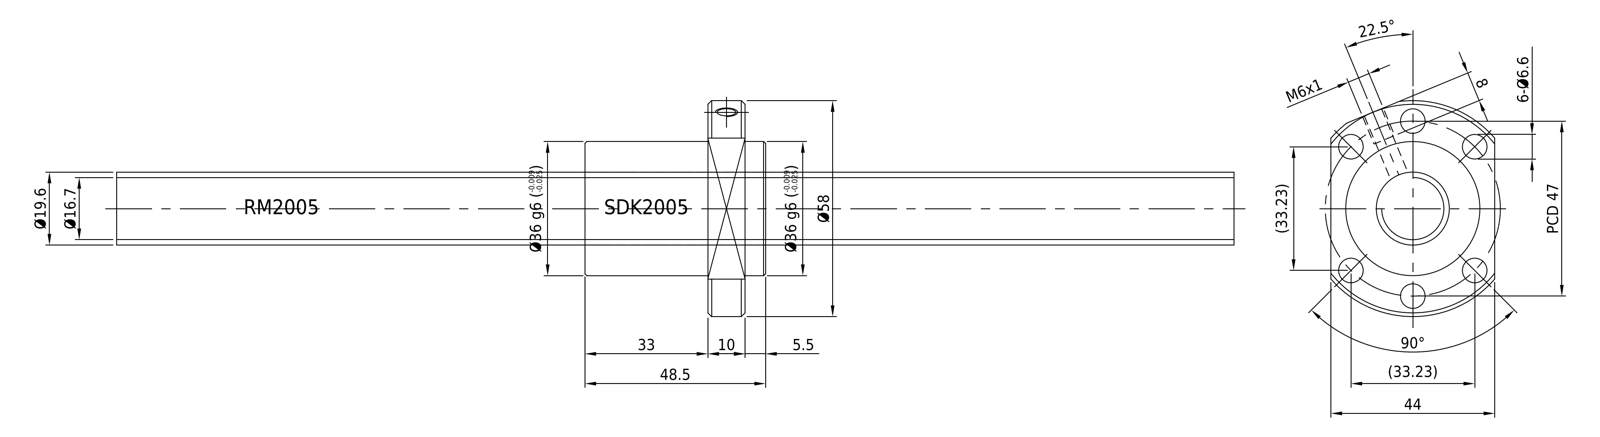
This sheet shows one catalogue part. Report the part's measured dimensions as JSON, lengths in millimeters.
{"part_name": "SDK2005; RM2005", "step_written_by": "SolidWorks 2013 (CONFIG_CONTROL_DESIGN)", "units": "millimeters", "bodies": {"solids": 2, "faces": 46, "planar": 9, "cylindrical": 27, "other": 10}, "overall_size": [300, 58, 44], "volume_mm3": 134721, "surface_area_mm2": 33035, "round_holes": [[6.6, 6], [3, 1], [5, 1], [20, 1]], "round_bosses_or_shafts": [[36, 1], [19.6, 1]], "partial_cylinders_radius": [[29, 1]], "face_to_face_distances": [10, 43, 33, 5.5, 15.5, 48.5, 125.75, 174.25, 44, 131.25], "hole_center_spacings": [23.5, 33.23, 17.98, 17.99, 43.42, 46.99, 23.49, 43.41]}
